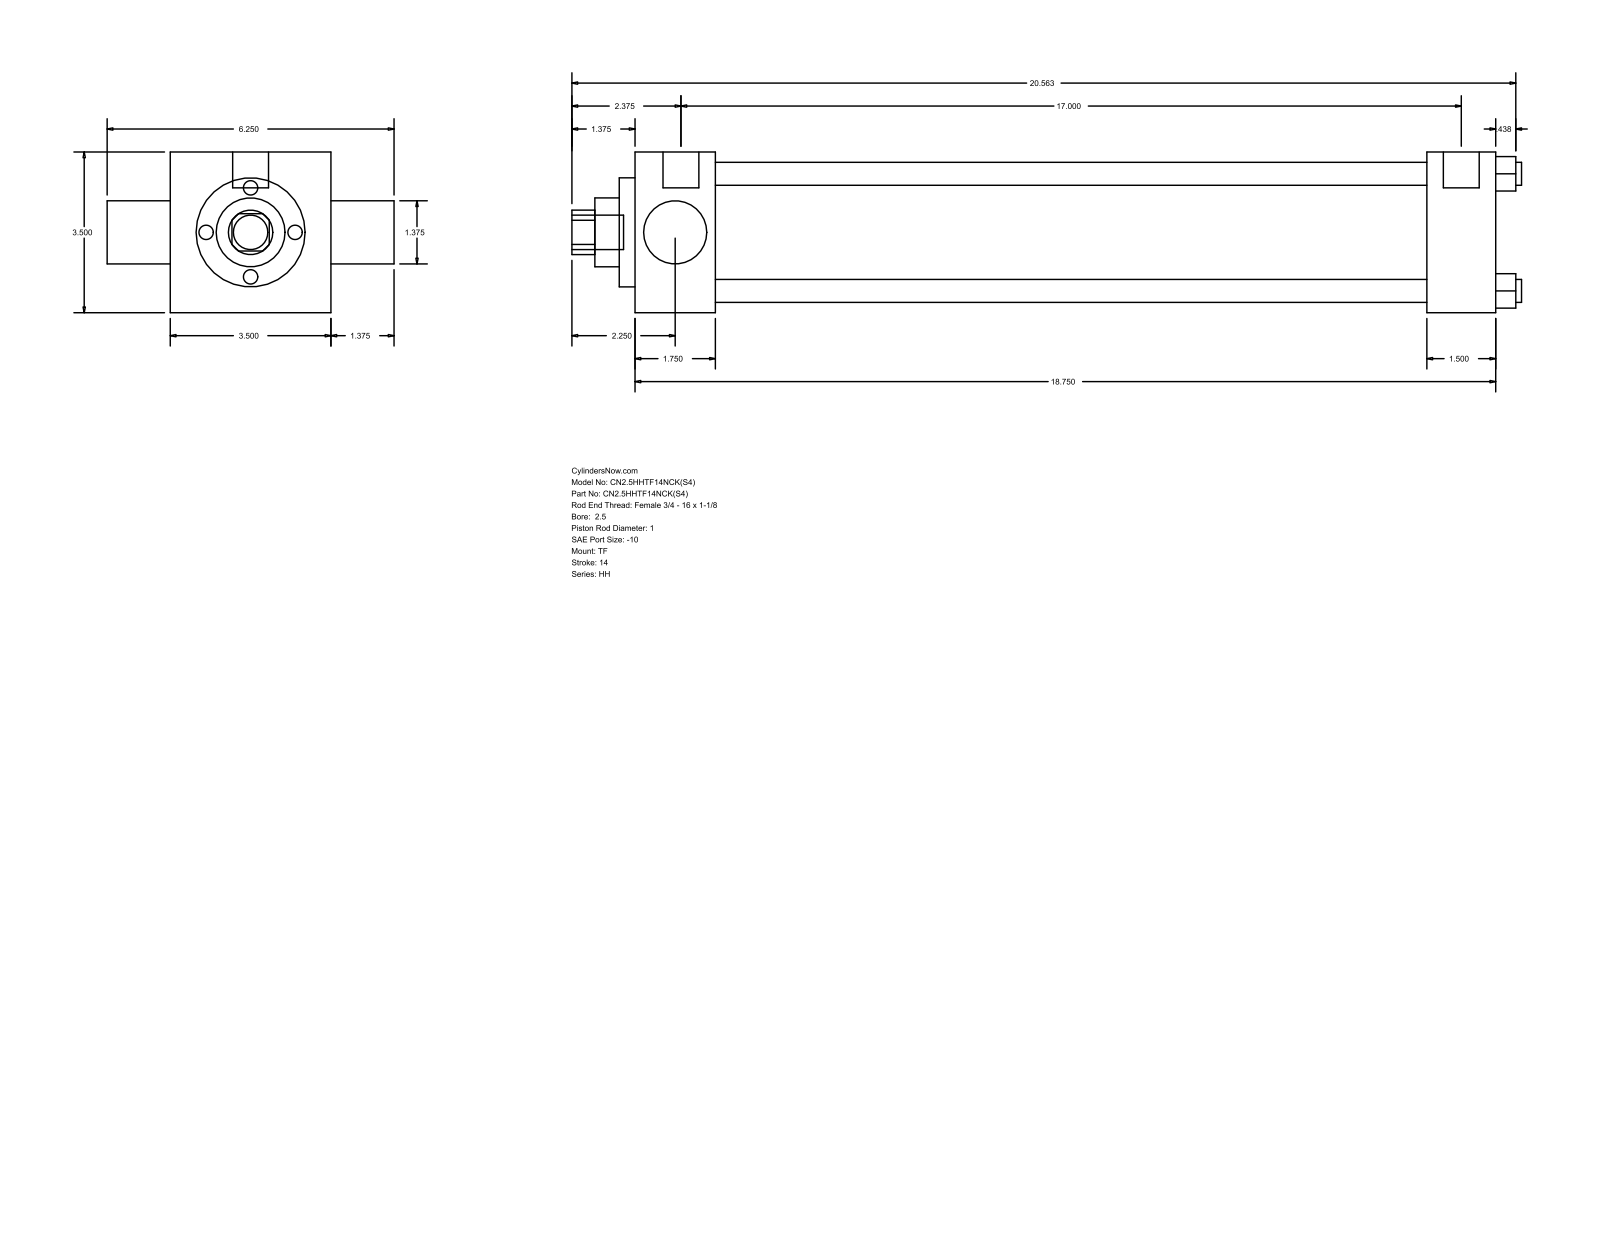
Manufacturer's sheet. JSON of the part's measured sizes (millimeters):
{"part_name": "HH_TF__0250_1", "step_written_by": "GSSL Pune (CONFIG_CONTROL_DESIGN)", "units": "millimeters", "bodies": {"solids": 0, "faces": 86, "planar": 61, "cylindrical": 25, "other": 0}, "overall_size": [525.46, 158.75, 88.9], "round_holes": [[12.7, 4], [25.4, 1], [34.92, 1], [38.1, 1], [60.33, 1], [73.03, 1]], "round_bosses_or_shafts": [[5.56, 3], [19.84, 2], [19.05, 1]], "partial_cylinders_radius": [[12.29, 1]], "face_to_face_distances": [88.9, 476.26, 44.46, 431.8, 438.15, 393.69, 38.11, 34.93, 123.83, 8.73], "hole_center_spacings": [45.79, 64.76, 91.58]}
